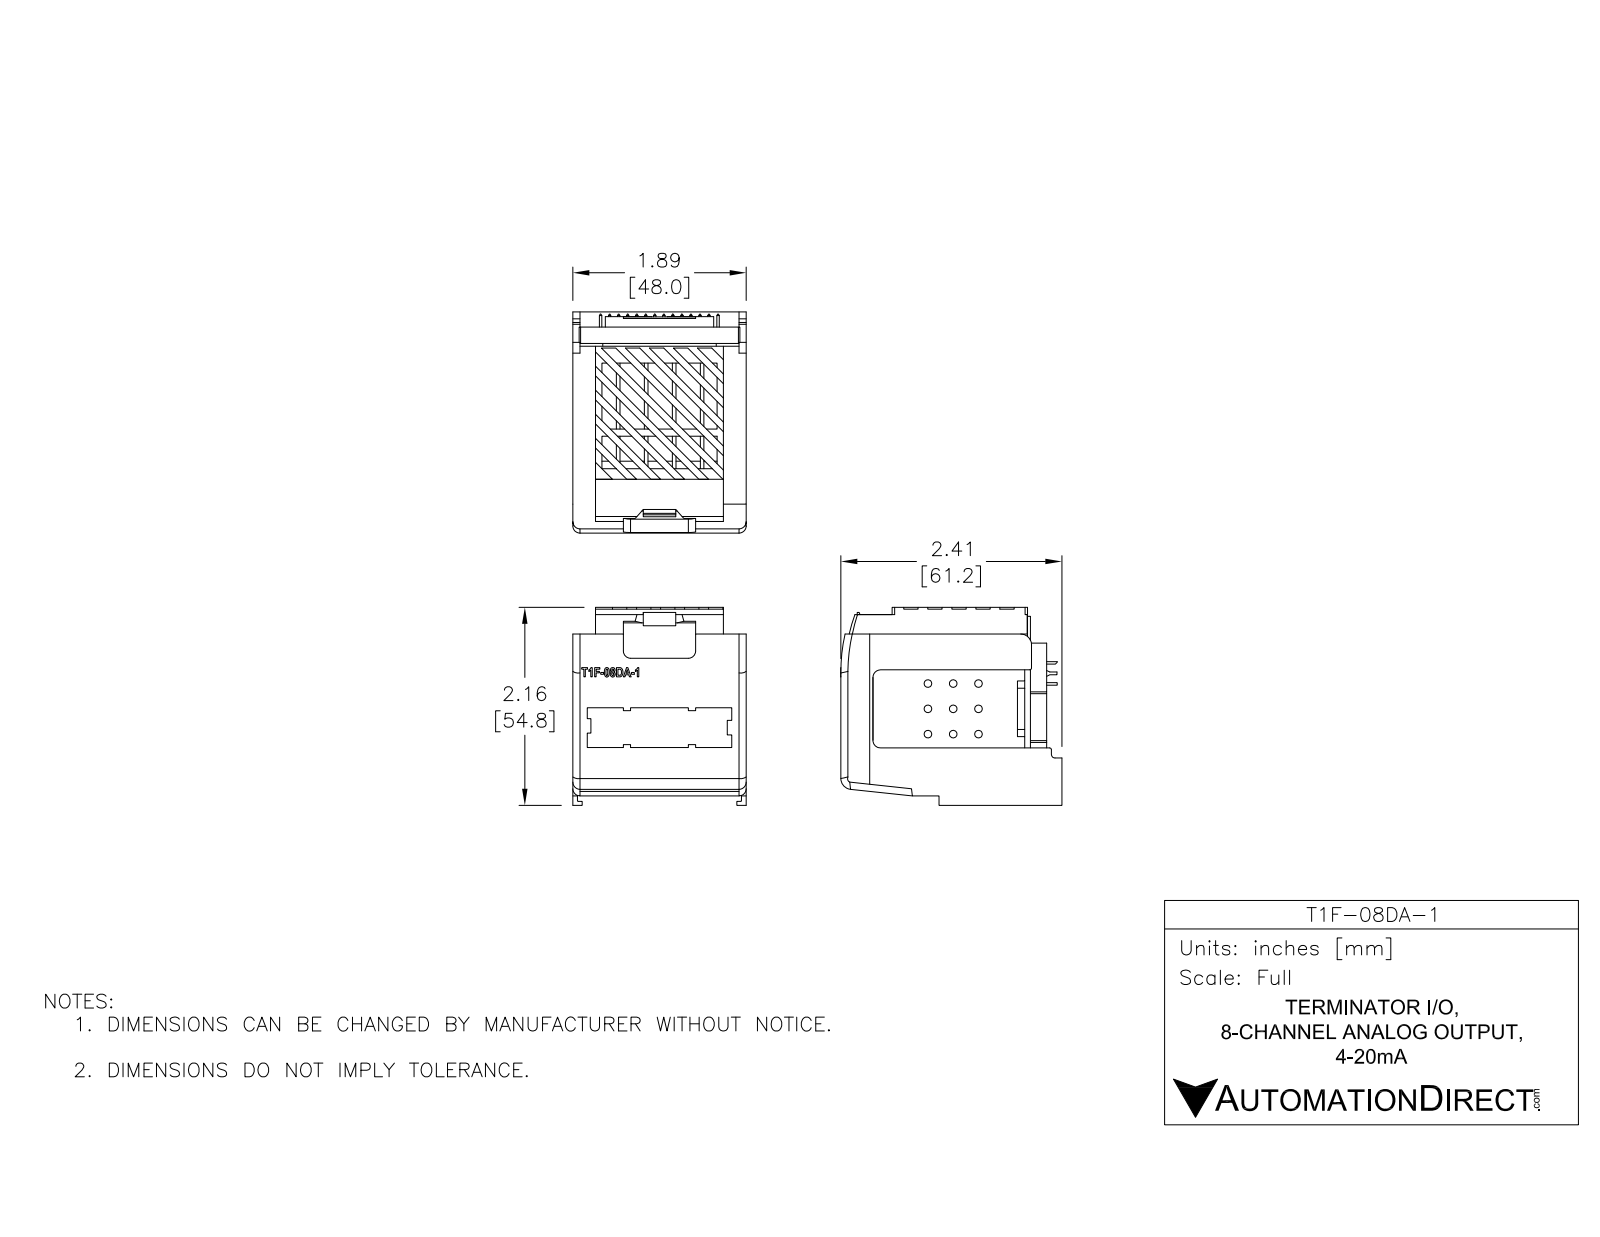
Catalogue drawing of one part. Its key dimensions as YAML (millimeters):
part_name: "T1F-08DA-1"
step_written_by: "SolidWorks 2013 (AUTOMOTIVE_DESIGN)"
units: millimeters
bodies: {solids: 1, faces: 556, planar: 422, cylindrical: 101, other: 33}
overall_size: [65.1, 61.36, 47.6]
volume: 30279
surface_area: 35941
round_holes:
  - {diameter: 3, count: 8}
round_bosses_or_shafts:
  - {diameter: 0.7, count: 28}
partial_cylinders:
  - {radius: 3.5, count: 10}
  - {radius: 1, count: 5}
  - {radius: 0.25, count: 3}
  - {radius: 0.55, count: 3}
  - {radius: 1.5, count: 2}
  - {radius: 8, count: 1}
  - {radius: 10, count: 1}
  - {radius: 18, count: 1}
face_to_face_distances: [2, 45.6, 47.6, 43.6, 55.35, 49.9, 6.55, 39.05, 59.8, 9.9]
hole_center_spacings: [5.2, 10.4, 15.6, 20.8, 26, 31.2, 36.4]
